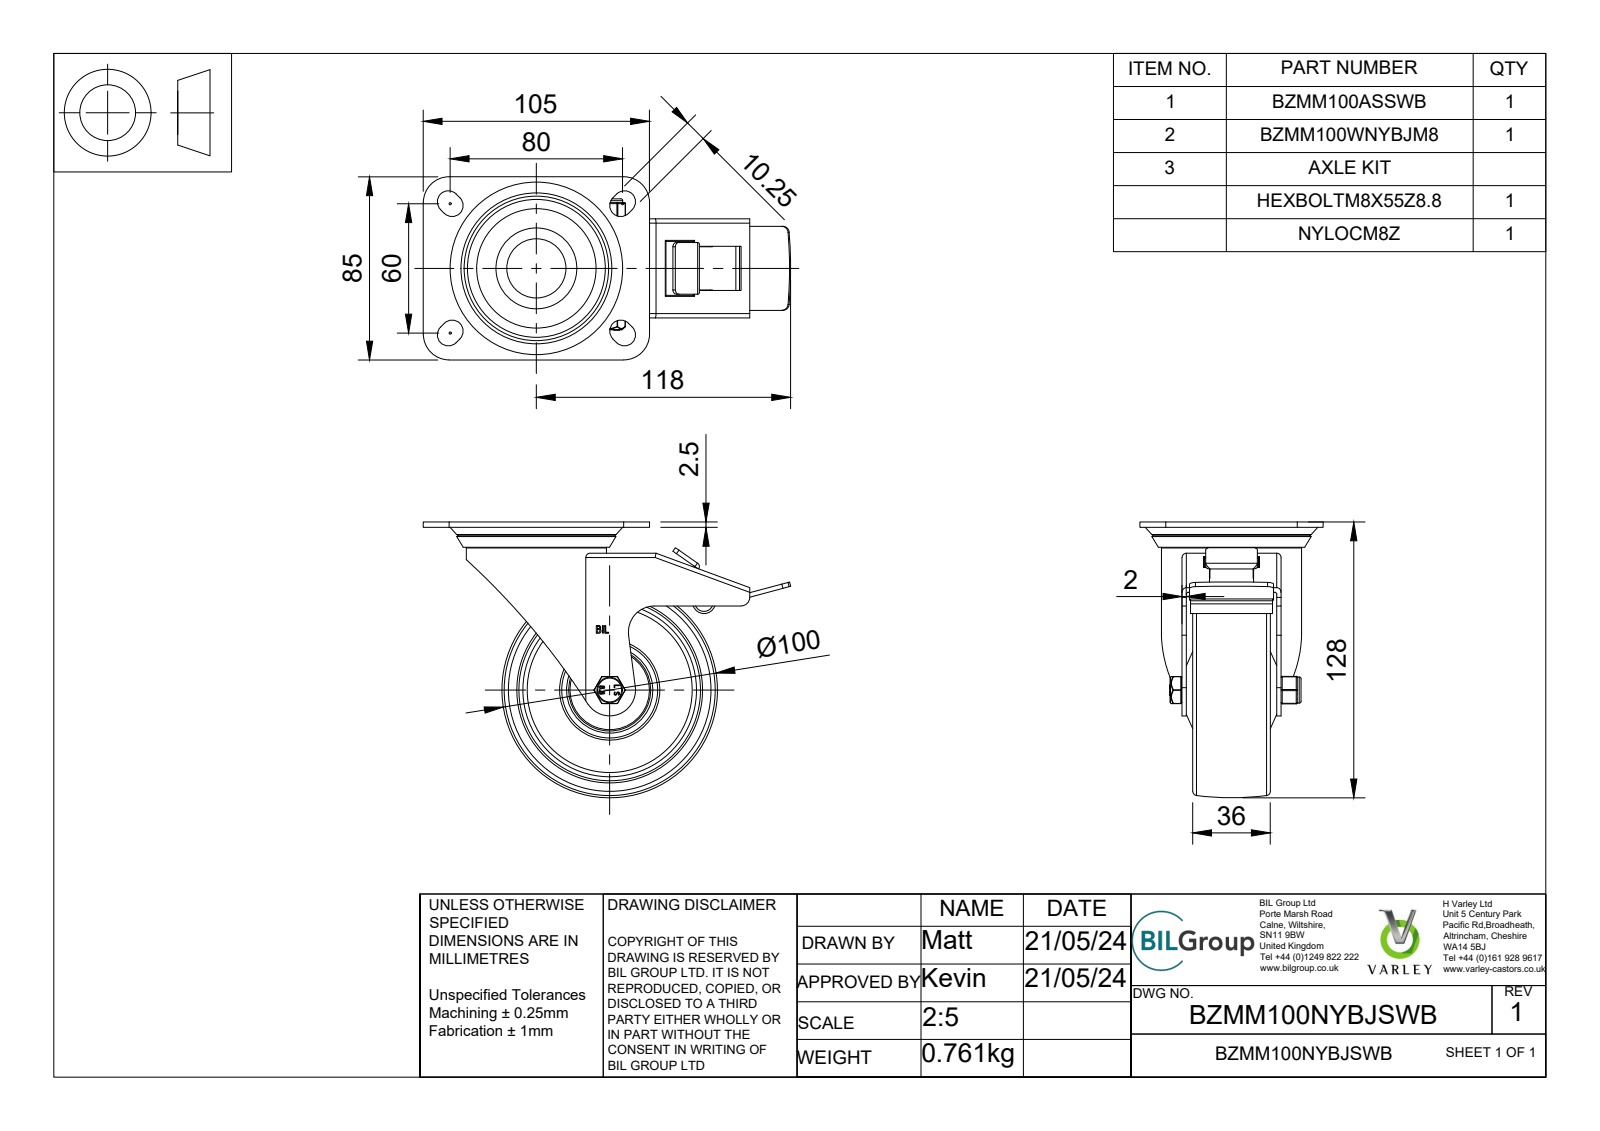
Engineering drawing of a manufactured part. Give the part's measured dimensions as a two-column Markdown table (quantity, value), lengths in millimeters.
| quantity | value |
| --- | --- |
| part name | BZMM100NYBJSWB v3; BZMM100WNYBJM8 v1; BZMM100WNYBJ; NYLON WHEEL (+8 more) |
| STEP written by | Autodesk Translation Framework v13.14.0.145 (AUTOMOTIVE_DESIGN) |
| units | millimeters |
| bodies | 48 solids, 940 faces (427 planar, 213 cylindrical, 300 other) |
| overall size | 170.5 × 128 × 85 |
| volume | 224 060 mm³ |
| surface area | 131 736 mm² |
| round holes (diameter × count) | 0.66 × 2, 8 × 1, 8.2 × 1, 8.6 × 1, 15 × 1, 20 × 1, 22.5 × 1, 25 × 1, 27.5 × 1, 30 × 1, 31 × 1, 32 × 1 |
| round bosses / shafts (diameter × count) | 65 × 1, 44.5 × 1, 38 × 1, 31.5 × 1, 30.5 × 1, 28 × 1, 23 × 1, 19 × 1 |
| partial cylindrical surfaces (radius × count) | 0.5 × 22, 0.25 × 12, 2 × 9, 5.12 × 8, 1 × 6, 12 × 6, 0.33 × 4, 0.64 × 4 |
| main face-to-face distances | 2, 26.75, 17.25, 24.75, 19.25, 44, 1, 2.5, 13, 7.5 |
| hole center spacings | 3.22, 2.49 |
